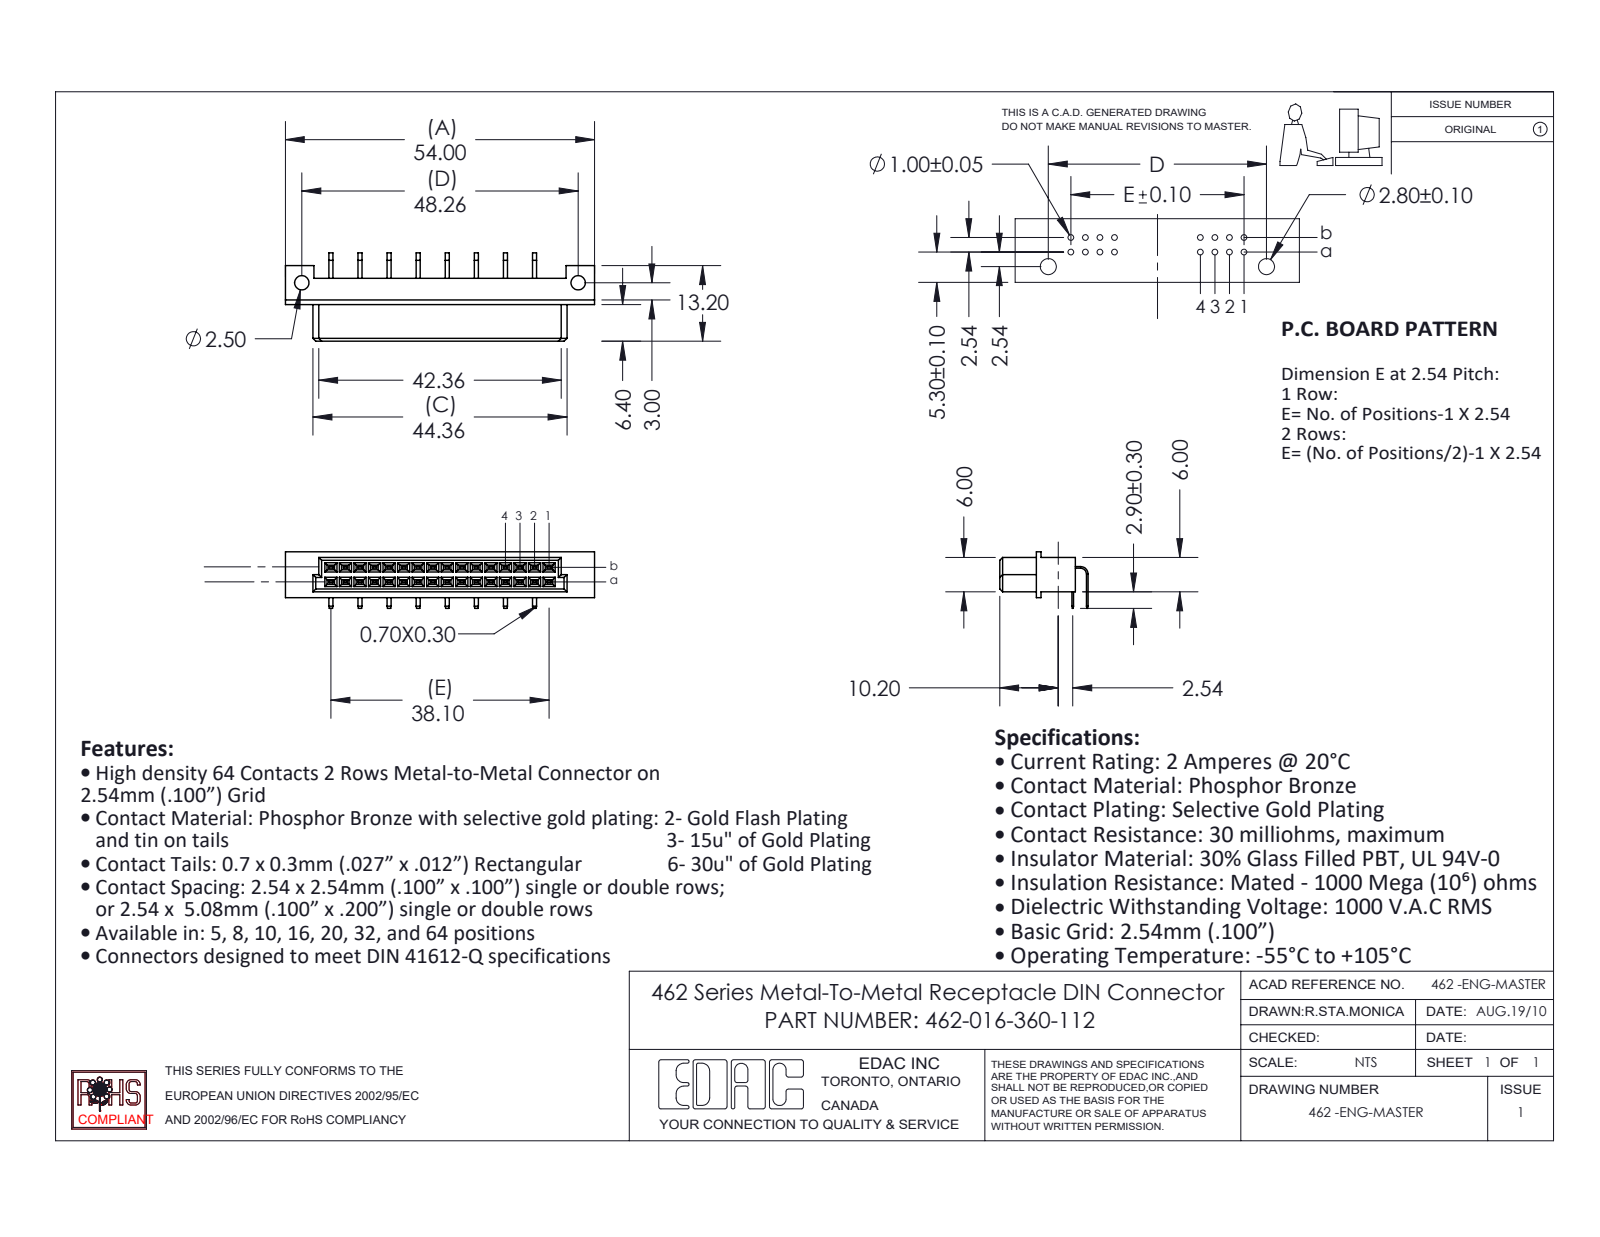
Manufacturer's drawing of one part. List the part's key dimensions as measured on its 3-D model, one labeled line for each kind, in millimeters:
Part name (STEP PRODUCT): 462-290-1; 462 Part_32; 462-016-360-112
STEP written by: SolidWorks 2020 (CONFIG_CONTROL_DESIGN)
Units: millimetres
Bodies: 17 solids, 675 faces (639 planar, 36 cylindrical, 0 other)
Overall size (bounding box): 54 × 13.2 × 9.9
Volume: 3 070 mm³ · Surface area: 3 621 mm²
Round holes (diameter × count): ⌀2.5 ×2
Partial cylindrical surfaces — rounded edges, fillets, slot ends (radius × count): R1.02 ×1, R1.32 ×1
Main face-to-face distances: 6, 2.54, 0.81, 4.6, 1.58, 4.42, 0.56, 1.88, 4.12, 0.55
Hole centre spacings: 48.26
